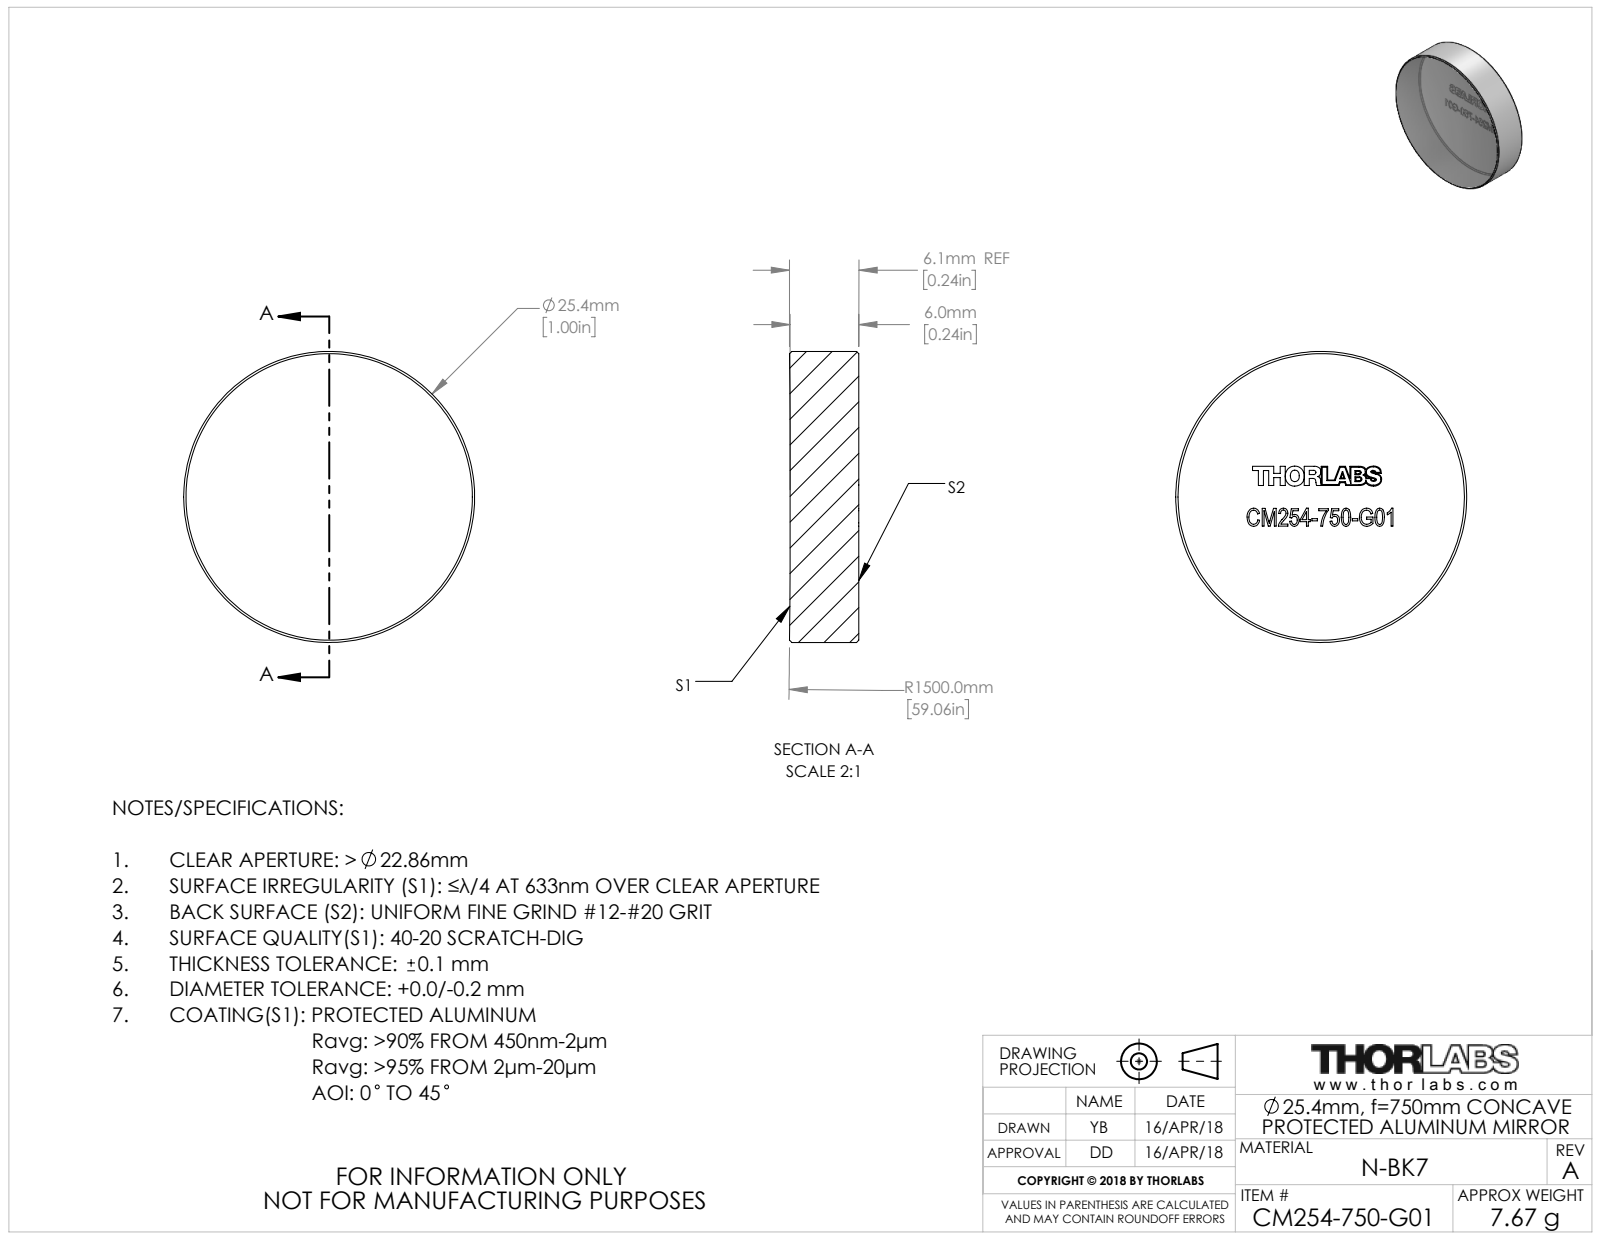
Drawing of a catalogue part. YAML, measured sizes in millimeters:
part_name: "TTN153308-E0W"
step_written_by: "SolidWorks 2018 (CONFIG_CONTROL_DESIGN)"
units: millimeters
bodies: {solids: 1, faces: 40, planar: 32, cylindrical: 2, other: 6}
overall_size: [25.4, 25.4, 6.05]
volume: 3051
surface_area: 1478
round_bosses_or_shafts:
  - {diameter: 25.4, count: 1}
